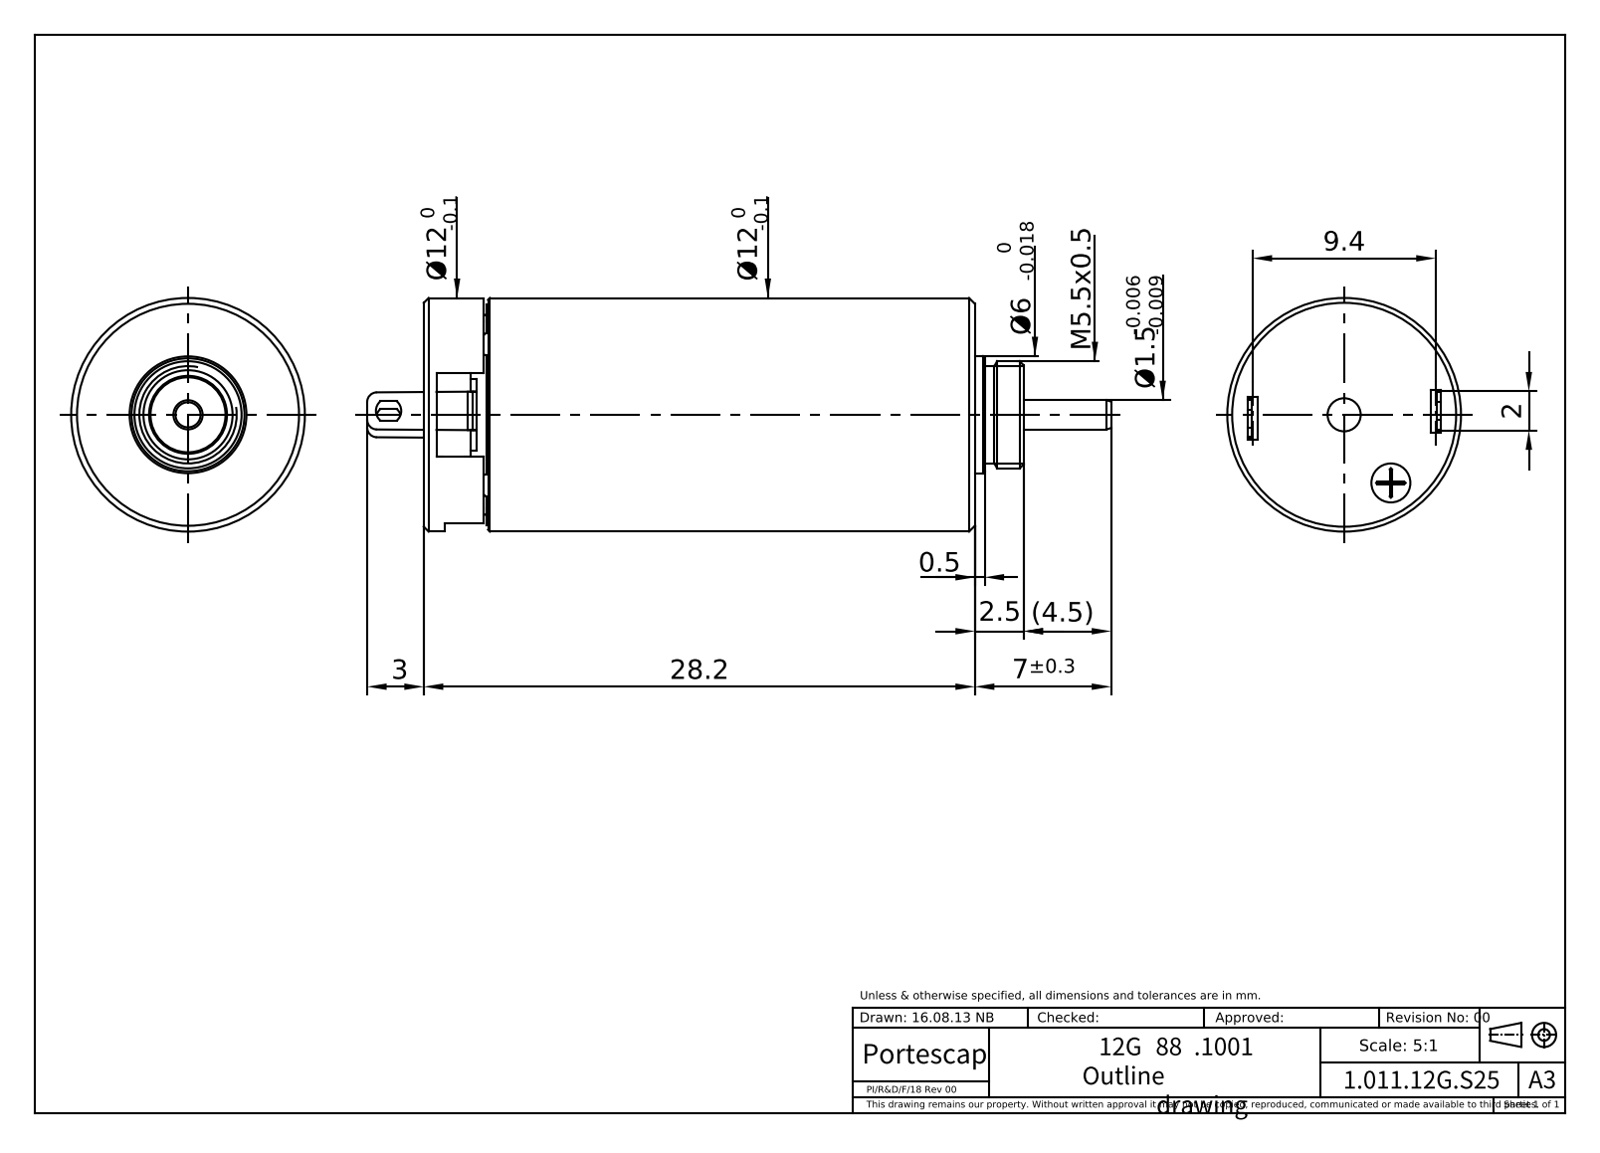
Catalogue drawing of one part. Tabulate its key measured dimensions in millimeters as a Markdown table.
| quantity | value |
| --- | --- |
| part name | 12G_88_201E_1001 |
| STEP written by | PRO/ENGINEER BY PARAMETRIC TECHNOLOGY CORPORATION, 2014310 (CONFIG_CONTROL_DESIGN) |
| units | millimeters |
| bodies | 1 solid, 233 faces (133 planar, 71 cylindrical, 29 other) |
| overall size | 38.11 × 12 × 12 |
| volume | 3 160 mm³ |
| surface area | 1 624 mm² |
| round holes (diameter × count) | 1.7 × 1, 2 × 1 |
| round bosses / shafts (diameter × count) | 12 × 1, 6 × 1, 5.5 × 1, 5.1 × 1, 1.5 × 1 |
| partial cylindrical surfaces (radius × count) | 0.5 × 8, 0.21 × 4, 1.9 × 4, 2 × 4, 0.65 × 2, 0.9 × 2, 0.91 × 2, 1.2 × 2 |
| main face-to-face distances | 28.3, 2.5, 2.4, 2.8, 0.4, 28.05, 28.4, 3.05, 0.65, 2.65 |
| hole center spacings | 4.24 |
